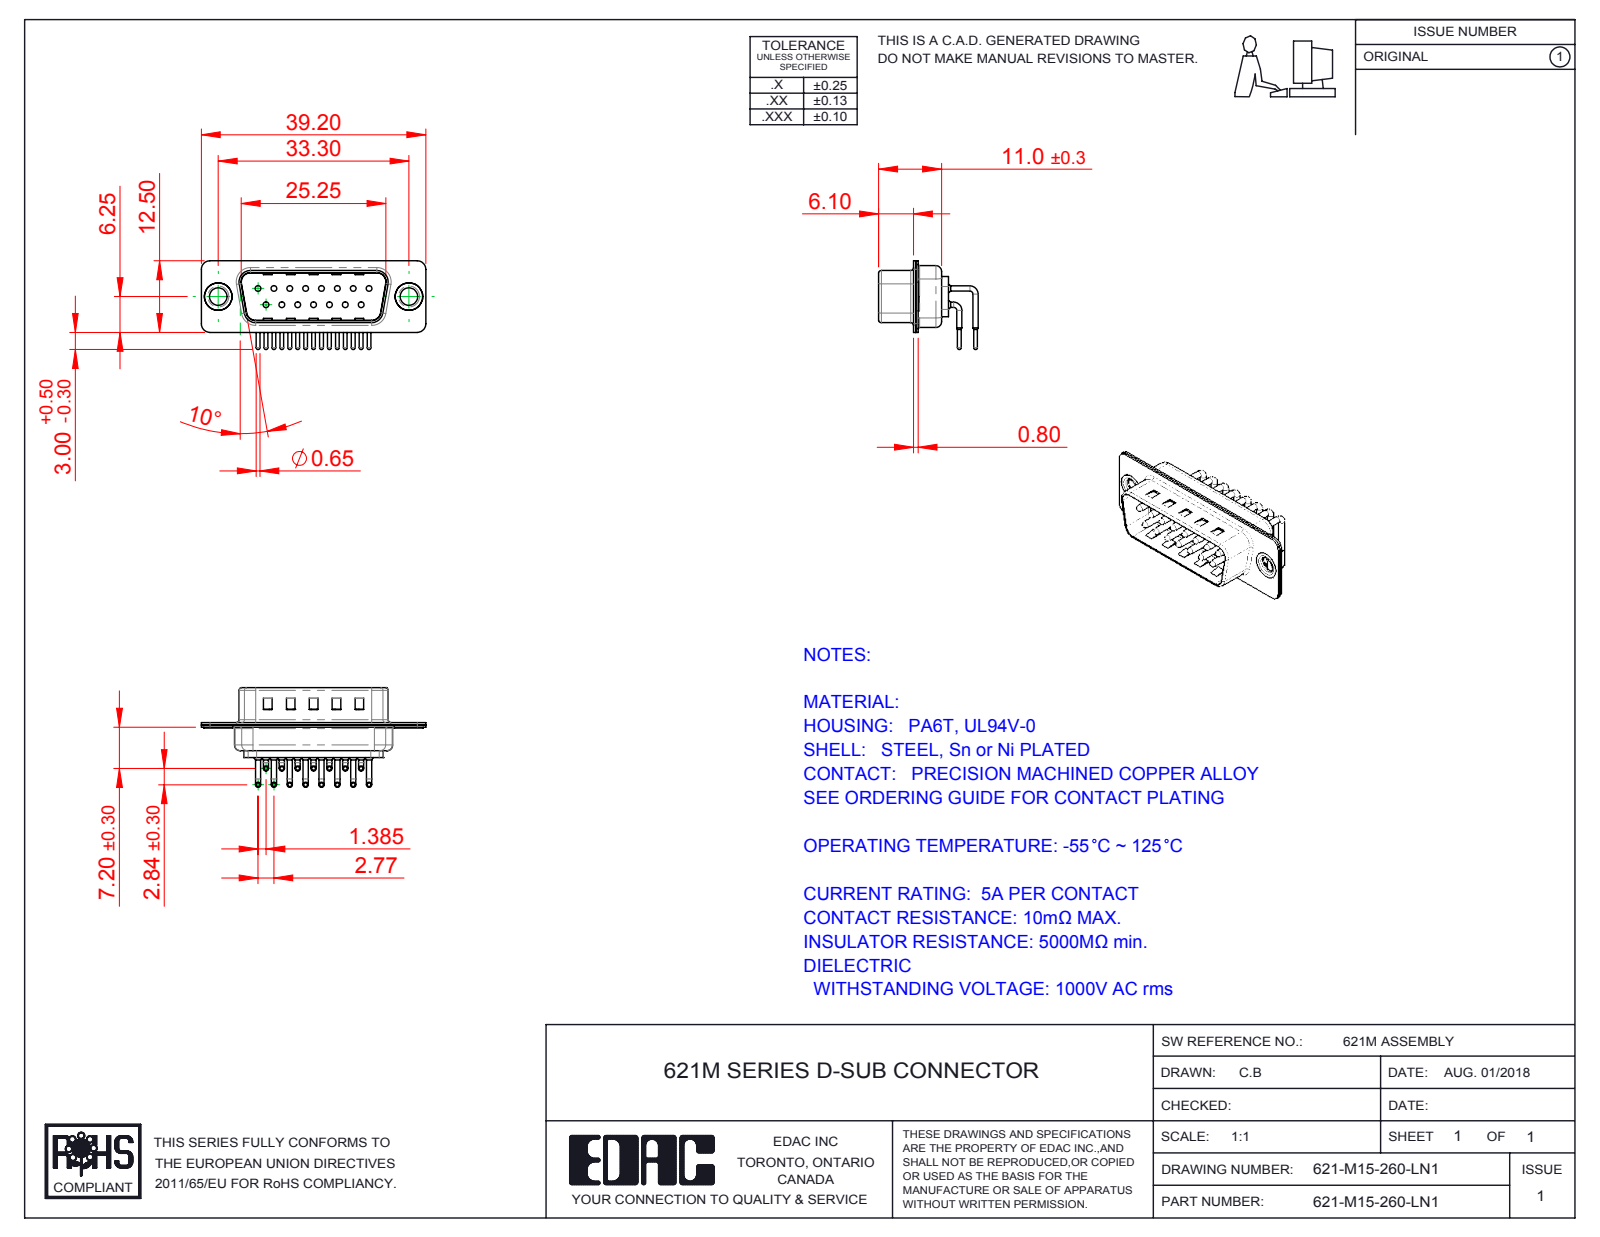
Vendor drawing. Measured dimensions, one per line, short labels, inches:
name: 621M Contact Row 2; 621M Housing_15 Contacts; 621M Shell Rear_15 Contacts; 621M Thru Hole Rivet (+3 more)
written by: SolidWorks 2016 (CONFIG_CONTROL_DESIGN)
unit: in
bodies: 20 solids, 1964 faces (1099 planar, 657 cylindrical, 208 other)
size: 1.543 × 0.685 × 0.61
volume: 0.113 in³; area: 7.922 in²
holes: 15× ⌀0.039, 15× ⌀0.067, 15× ⌀0.079, 2× ⌀0.12, 2× ⌀0.157, 2× ⌀0.189
bosses: 30× ⌀0.035, 15× ⌀0.059, 15× ⌀0.026, 2× ⌀0.197, 2× ⌀0.193, 2× ⌀0.14
rounds: 16× R0.059, 15× R0.04, 12× R0.079, 8× R0.02, 8× R0.063, 4× R0.01, 4× R0.024, 4× R0.026
face distances: 0.016, 0.033, 0.376, 0.343, 0.049, 0.031, 0.409, 0.059, 0.014, 0.075
hole spacings: 0.124, 0.109, 0.218, 0.327, 0.436, 0.198, 0.198, 0.294
